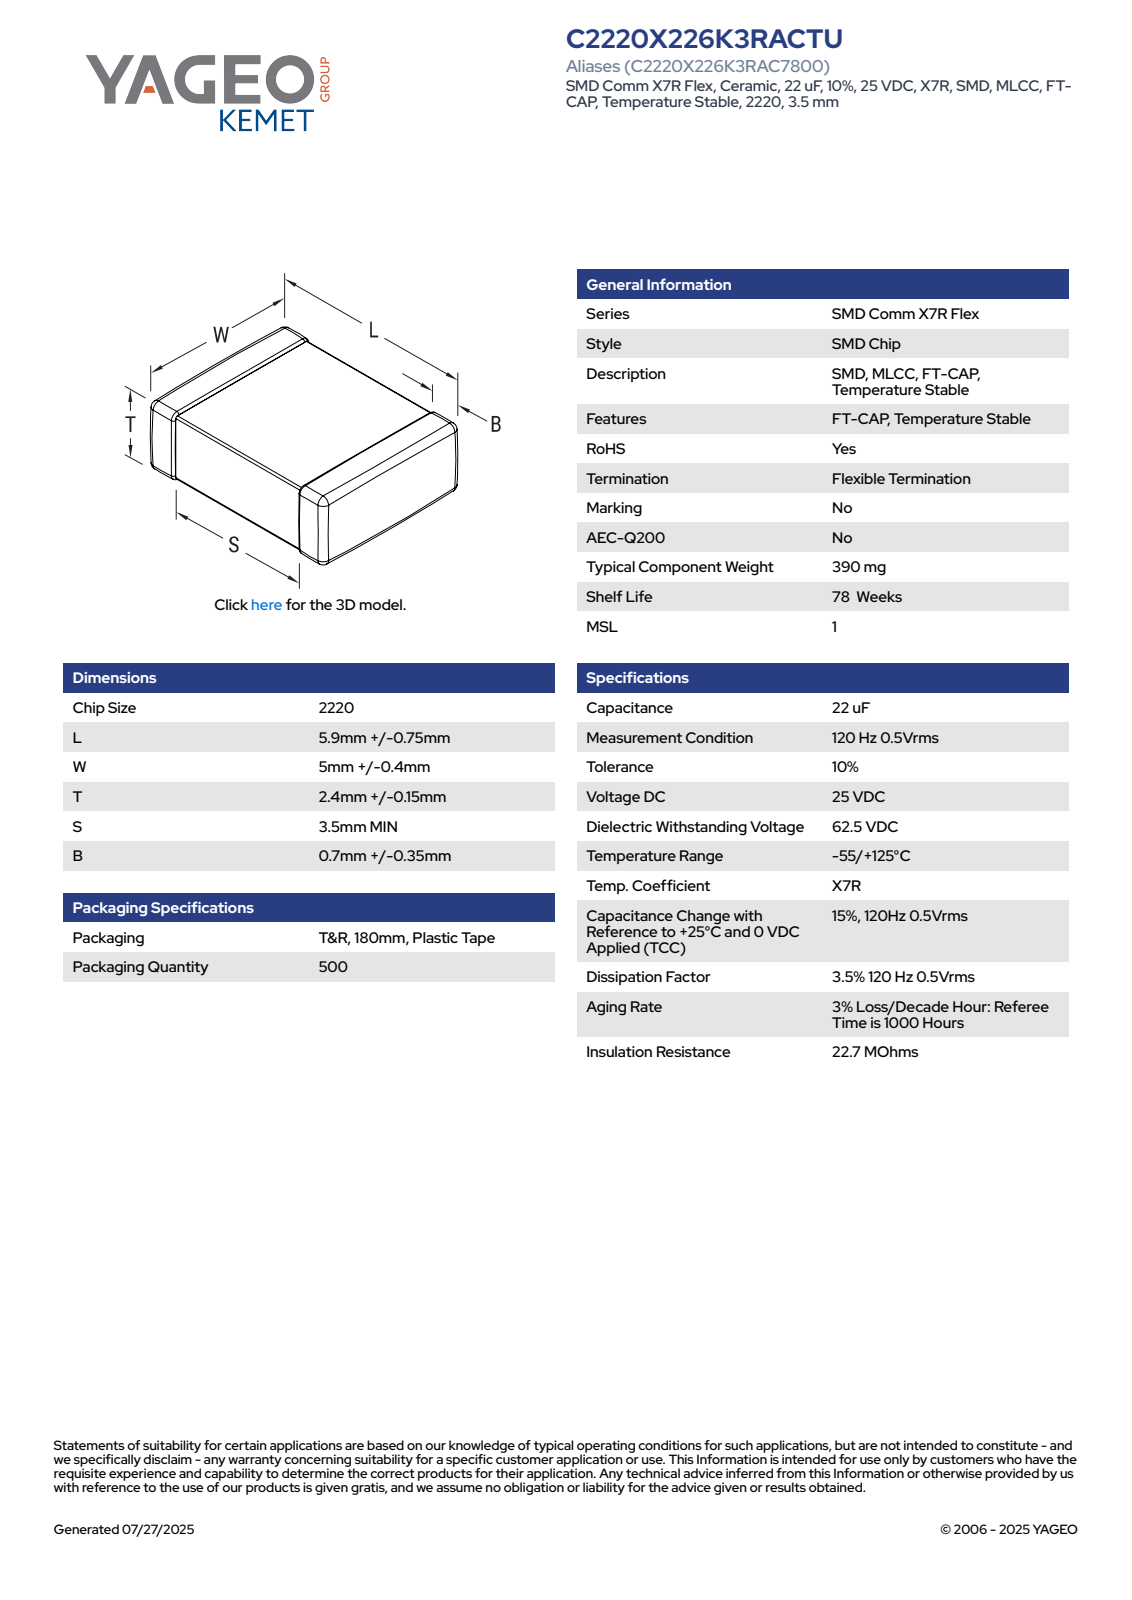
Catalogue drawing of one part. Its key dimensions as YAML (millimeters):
part_name: "CCS_CCSTDNOS_2220_L6.65W5.4T2.55B1.05"
step_written_by: "SolidWorks 2014 (AUTOMOTIVE_DESIGN)"
units: millimeters
bodies: {solids: 4, faces: 121, planar: 71, cylindrical: 34, other: 16}
overall_size: [6.65, 5.4, 2.55]
volume: 83
surface_area: 130
partial_cylinders:
  - {radius: 0.11, count: 24}
face_to_face_distances: [2.33, 2.44, 6.65, 5.18, 2.55, 5.29, 5.4, 2.51, 2.78, 2.62]
